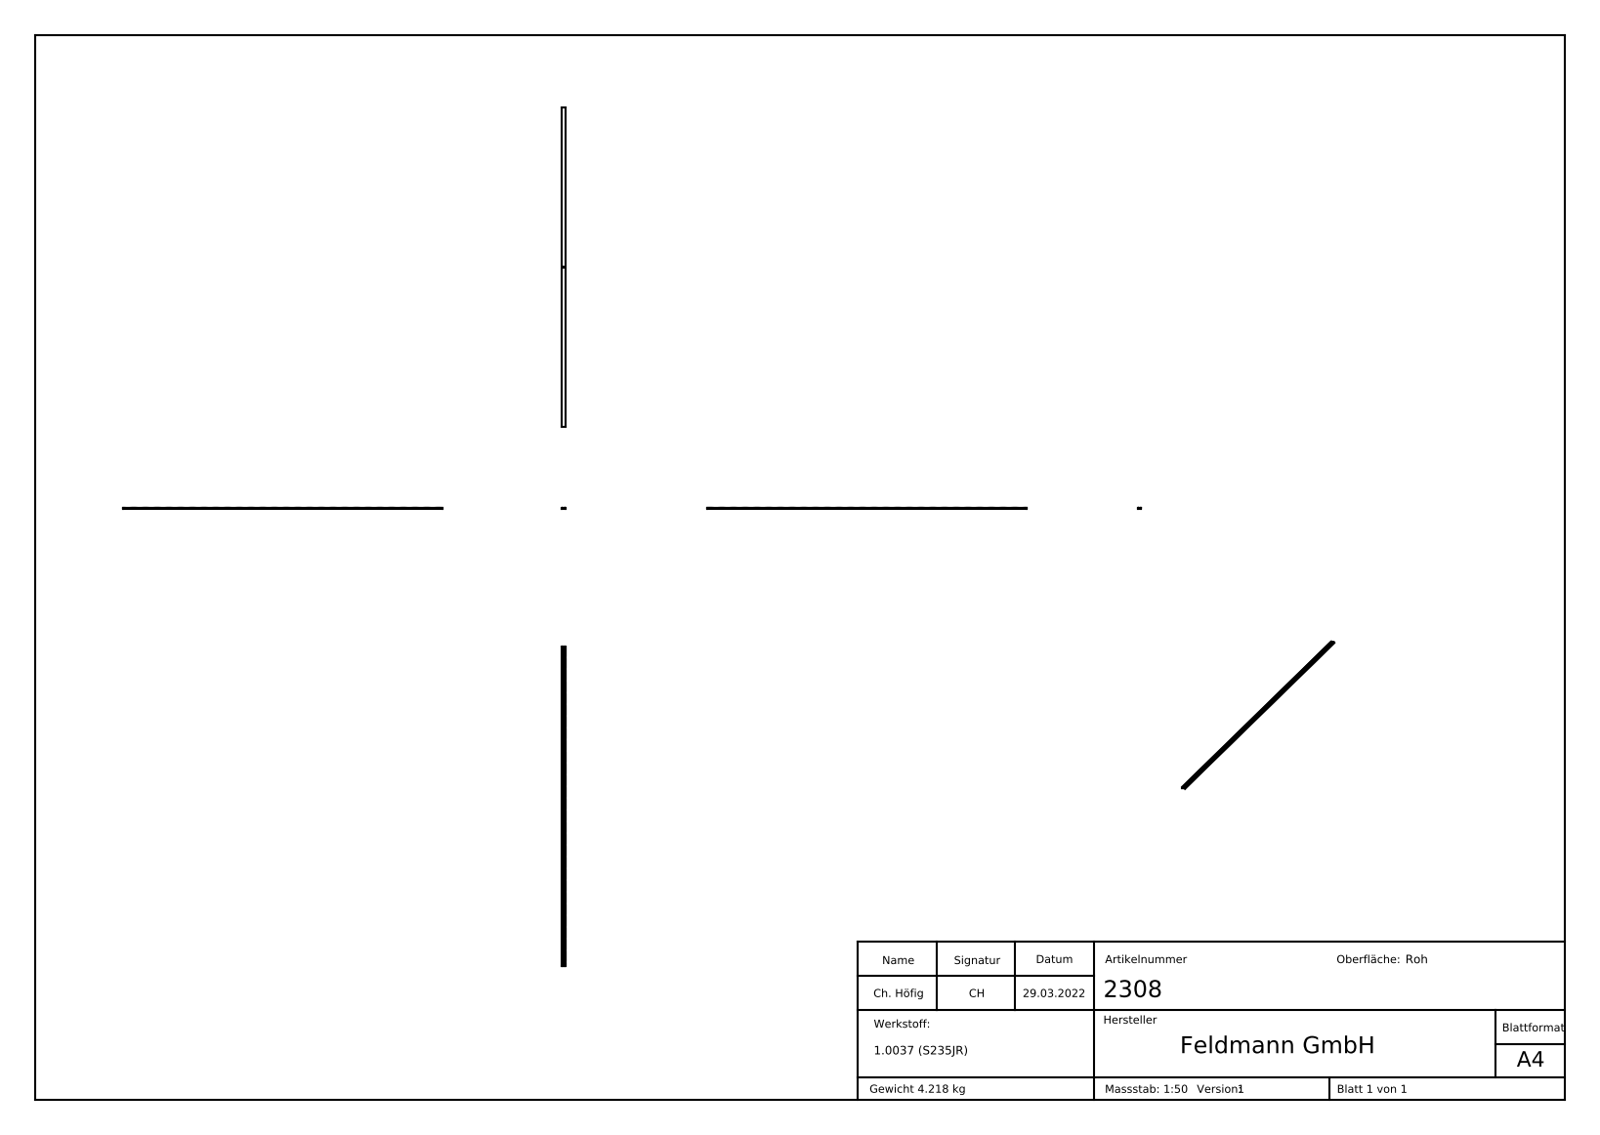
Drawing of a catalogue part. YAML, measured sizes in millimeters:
part_name: "2308"
step_written_by: "SolidWorks 2018 (CONFIG_CONTROL_DESIGN)"
units: millimeters
bodies: {solids: 1, faces: 1426, planar: 1310, cylindrical: 2, other: 114}
overall_size: [3000, 30, 8]
volume: 540725
surface_area: 228613
partial_cylinders:
  - {radius: 3.52, count: 2}
face_to_face_distances: [5, 30, 14.84, 3.71, 48.23, 11.13, 29.68, 63.07, 33.39, 18.55]
